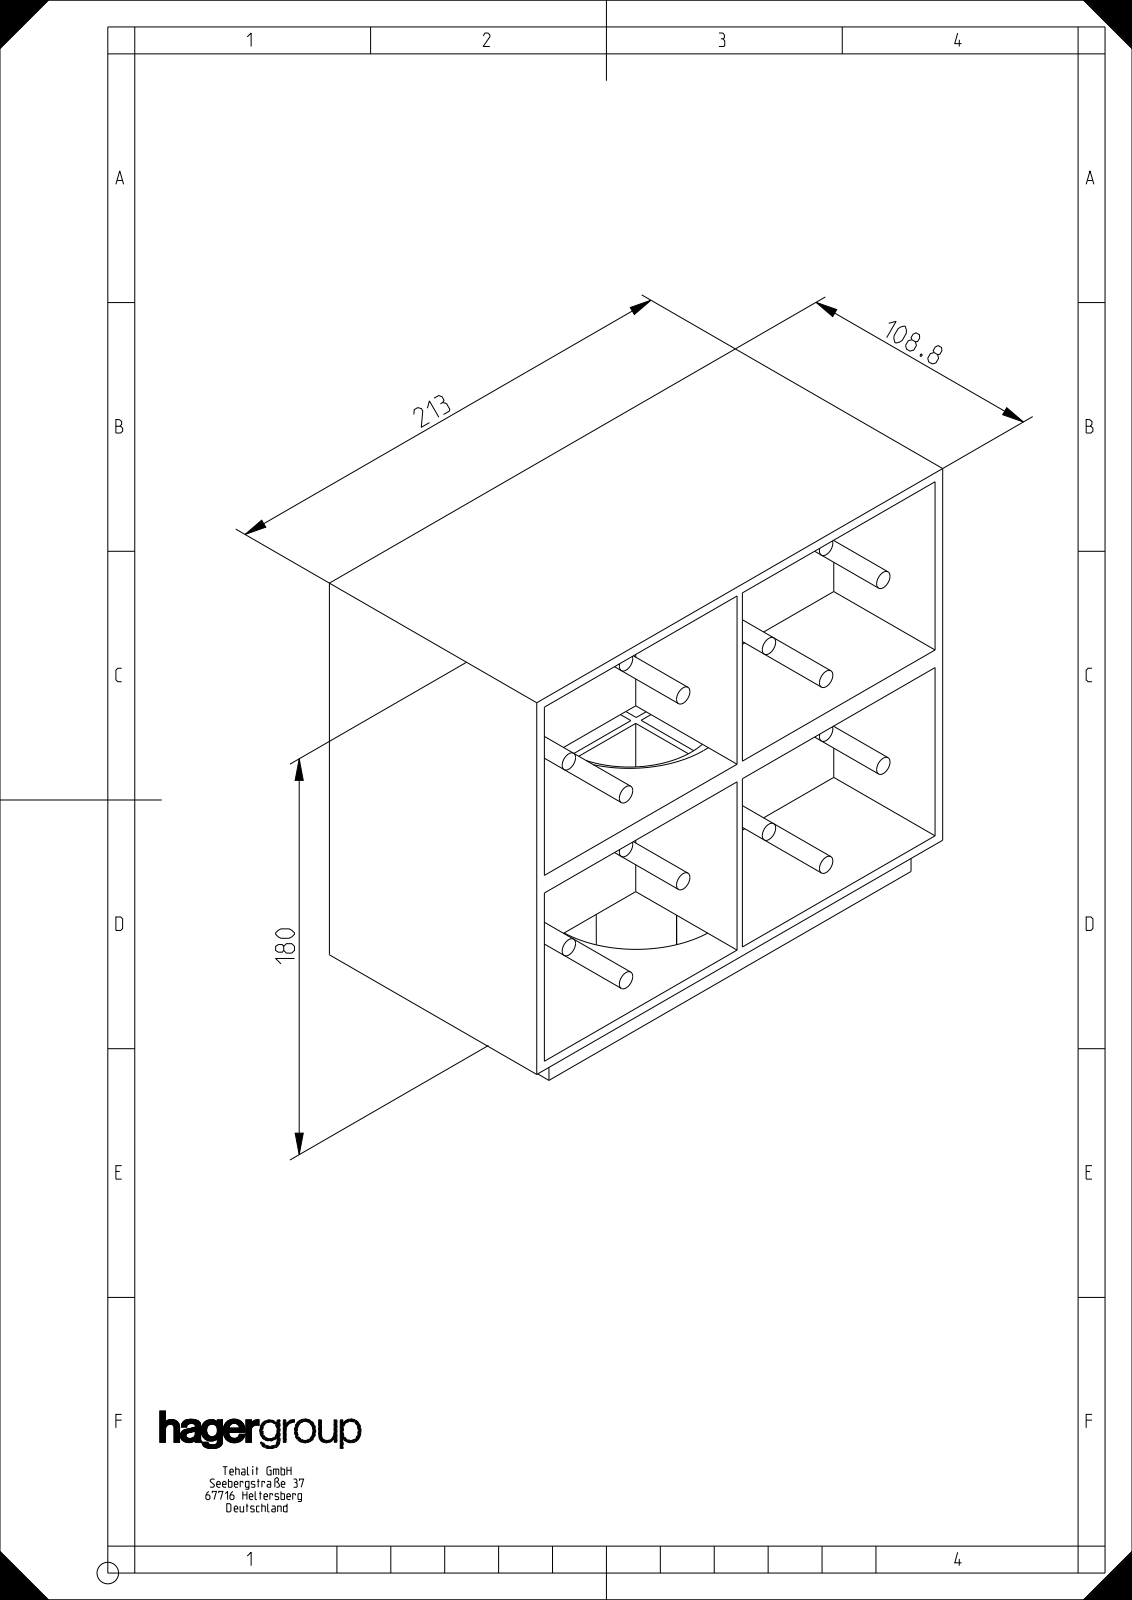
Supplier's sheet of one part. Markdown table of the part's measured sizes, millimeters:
| quantity | value |
| --- | --- |
| part name | GBZ89005KUN |
| STEP written by | CREO PARAMETRIC BY PTC INC, 2022024 (AUTOMOTIVE_DESIGN) |
| units | millimeters |
| bodies | 1 solid, 169 faces (99 planar, 70 cylindrical, 0 other) |
| overall size | 213 × 180 × 108.8 |
| volume | 807 321 mm³ |
| surface area | 340 473 mm² |
| round holes (diameter × count) | 78 × 2, 65 × 1 |
| round bosses / shafts (diameter × count) | 7 × 16 |
| main face-to-face distances | 4, 84.5, 76.5, 209, 105.1, 107.9, 101.1, 103.9, 2.55, 80.5 |
| hole center spacings | 4.02 |
